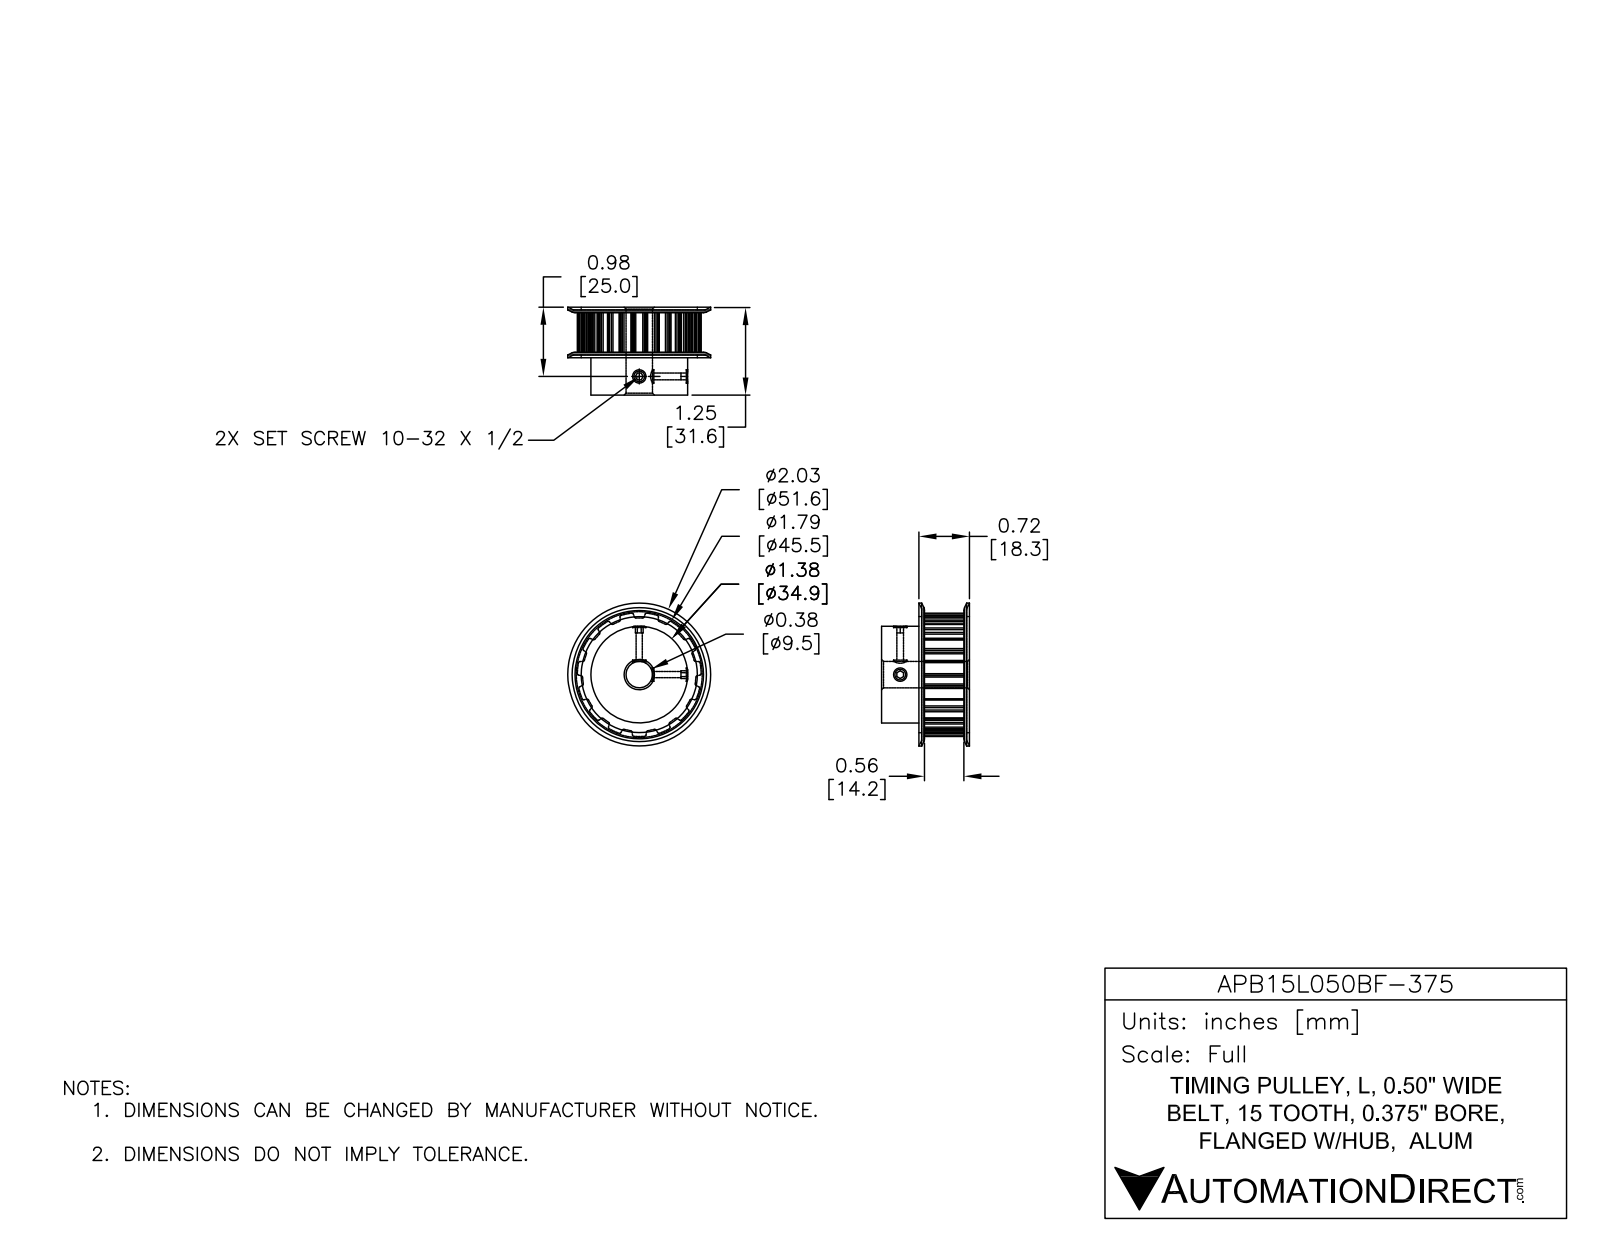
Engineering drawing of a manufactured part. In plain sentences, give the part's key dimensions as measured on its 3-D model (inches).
The part is named "APB15L050BF-375". Its 3-D file was written by "SolidWorks 2014 (AUTOMOTIVE_DESIGN)". It is 1 solid with 134 faces: 51 planar, 61 cylindrical and 22 other. Overall it measures 2.031 by 2.031 by 1.25 inches. Its volume is 2.356 cubic inches and its surface area 16.48 square inches. Round holes: 2 of diameter 0.088, 1 of diameter 0.375. Round bosses or shafts: 1 of diameter 1.375. Partial cylindrical surfaces (rounded edges, fillets, slot ends): 30 of radius 0.015, 1 of radius 0.825. The main face-to-face distances are 1.25, 0.68, 0.57, 0.04, 0.64, 1.21, 0.04, 0.6, 0.08, 1.17.
